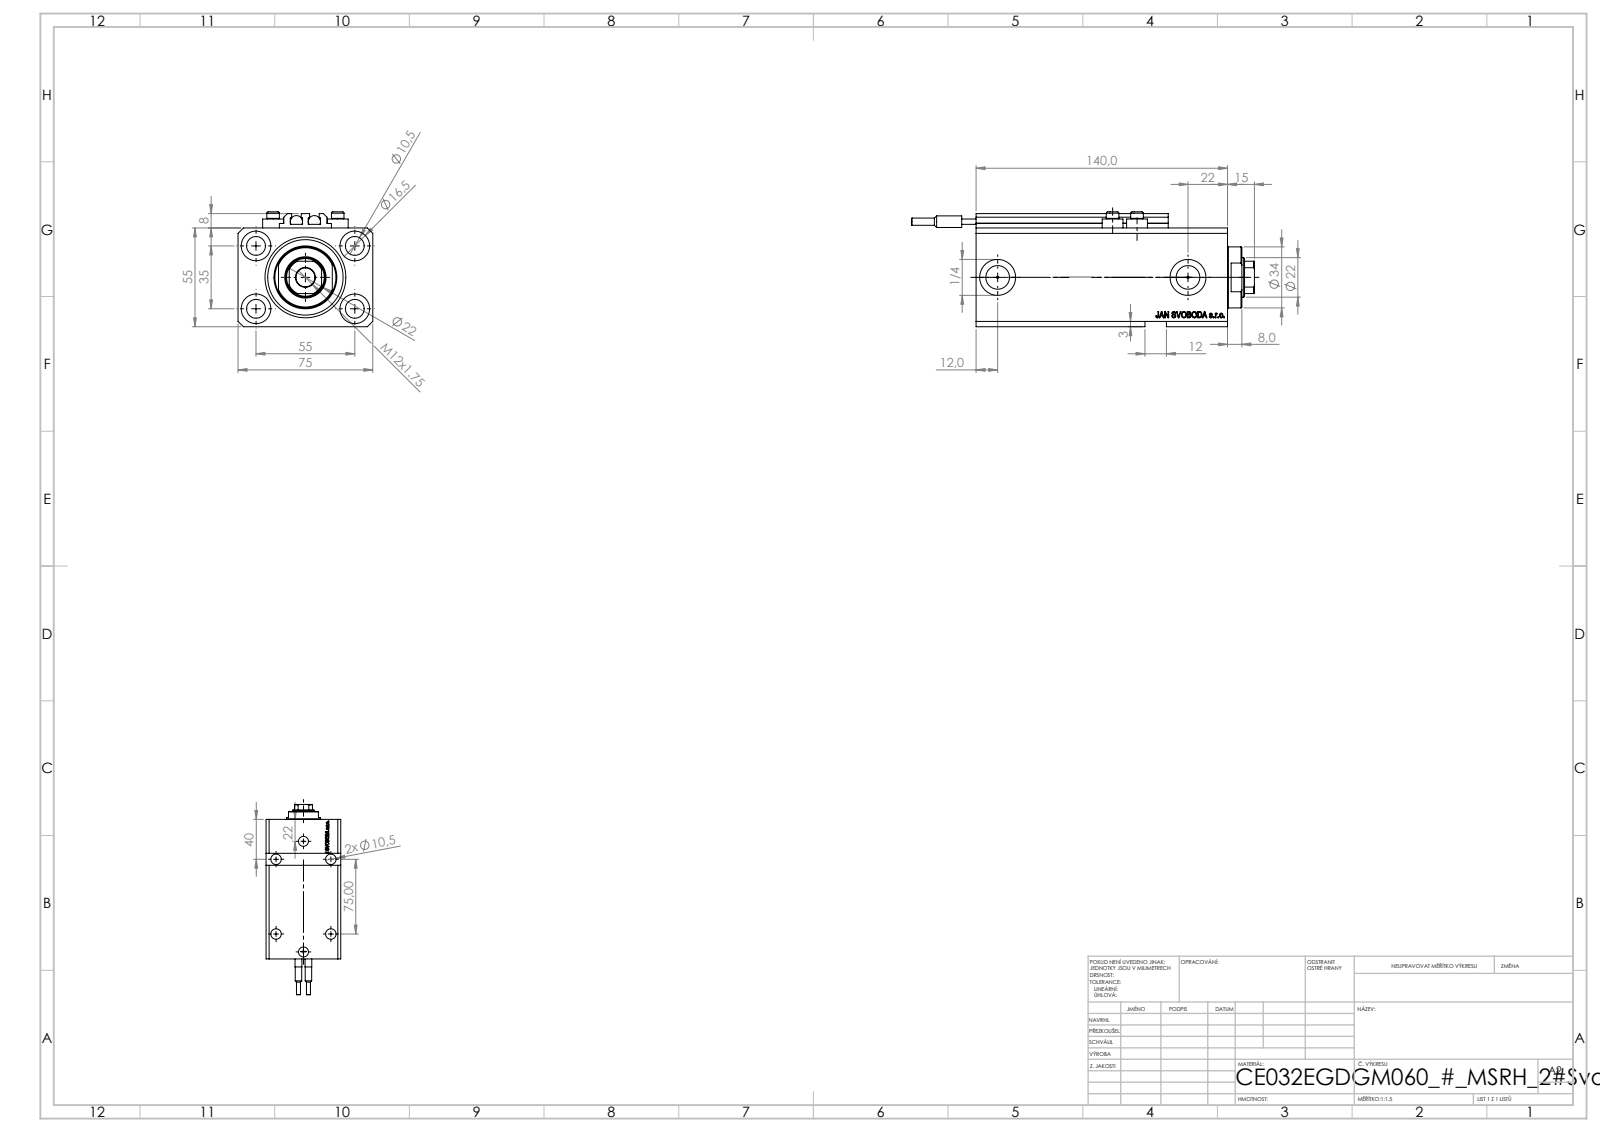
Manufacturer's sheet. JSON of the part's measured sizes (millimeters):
{"part_name": "V250CE_E_Body; ALLEN BOLT V250CE; V250CE_VC_E; V250CE_C_VCP (+1 more)", "step_written_by": "SolidWorks 2019 (CONFIG_CONTROL_DESIGN)", "units": "millimeters", "bodies": {"solids": 10, "faces": 1152, "planar": 550, "cylindrical": 170, "other": 432}, "overall_size": [191, 75, 64], "volume_mm3": 485172, "surface_area_mm2": 119202, "round_holes": [[10.5, 9], [1.25, 4], [4, 4], [16.5, 4], [10, 2], [13.16, 2], [20, 2], [22, 1], [32, 1], [45, 1]], "round_bosses_or_shafts": [[11.6, 4], [7, 4], [6.8, 2], [6.5, 2], [4, 2], [34, 1]], "partial_cylinders_radius": [[0.2, 10], [10.5, 1]], "face_to_face_distances": [55, 75, 3, 57, 15, 9.9, 140, 125, 2, 2.5], "hole_center_spacings": [32.6, 32.87, 55, 96.98, 13.6, 14.09, 25.81, 32.58]}
